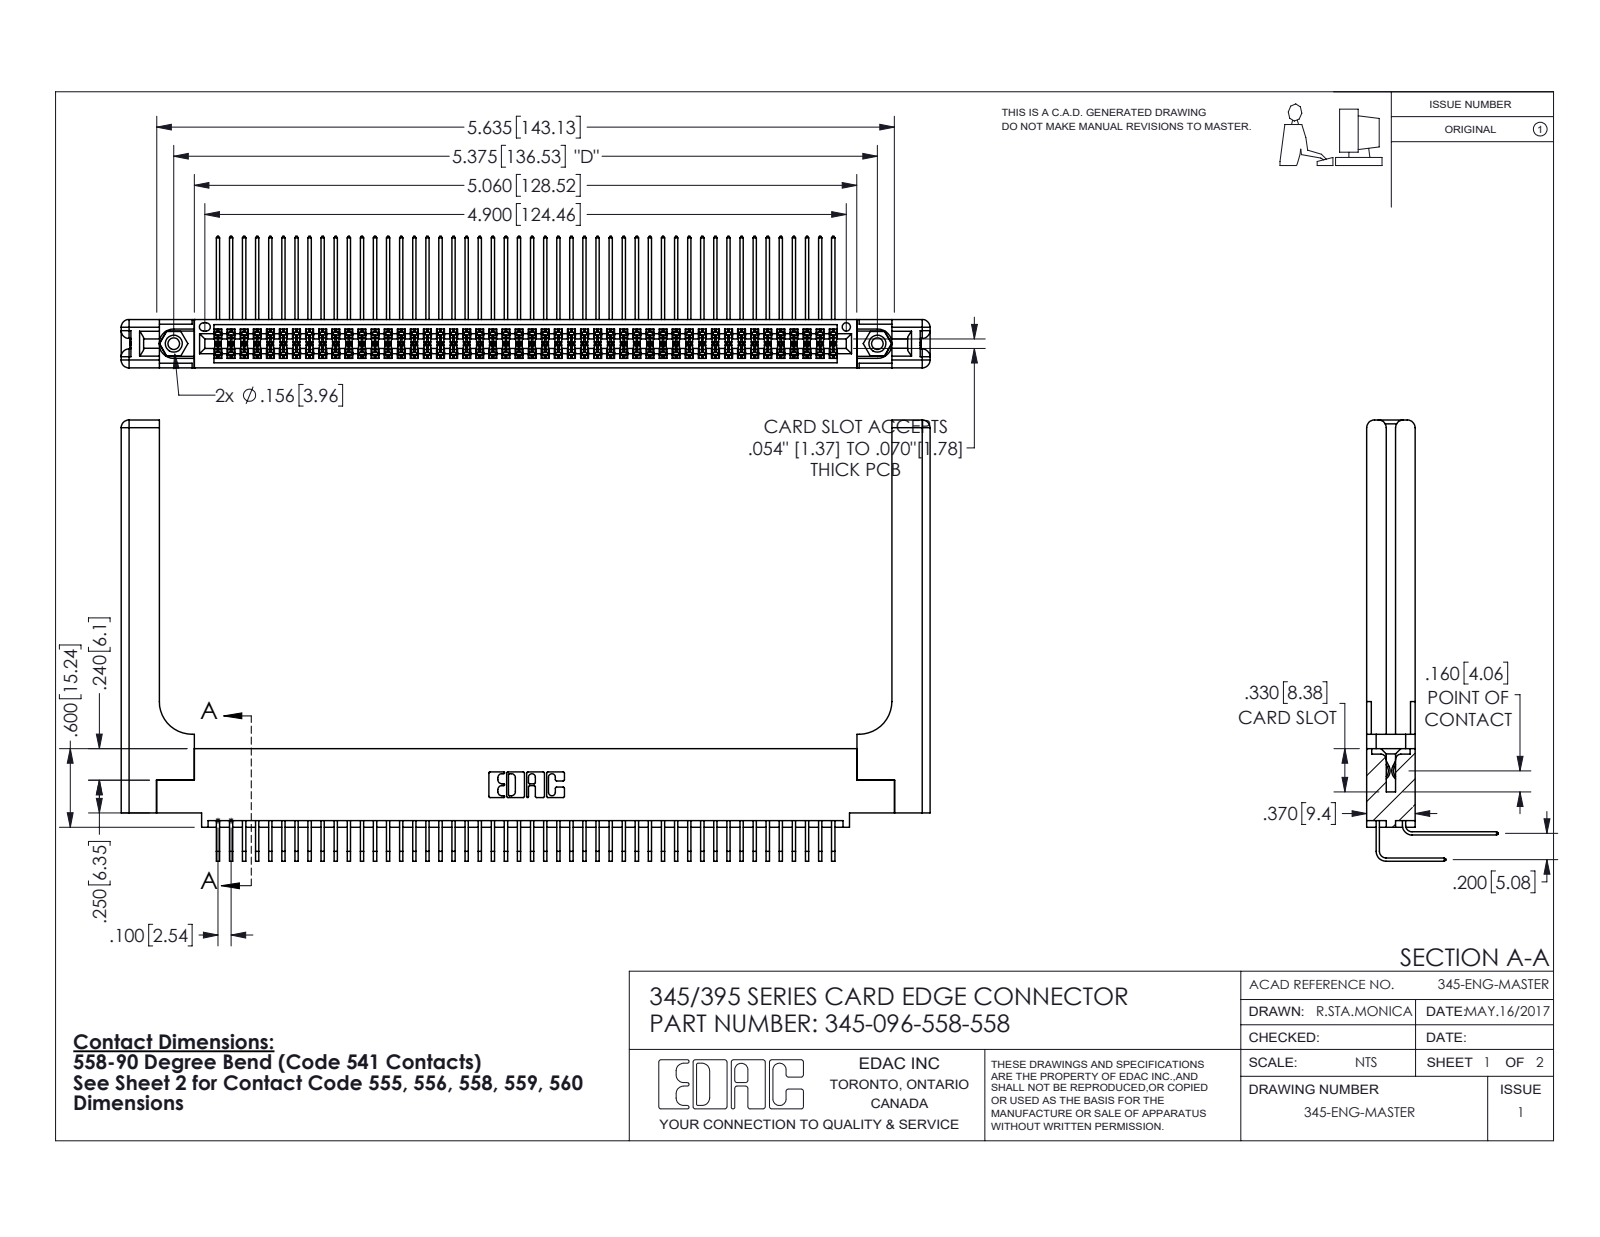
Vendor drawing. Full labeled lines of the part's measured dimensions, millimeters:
Part name (STEP PRODUCT): 345-096-558-558; 345-220-058_345-220-058; 345-250-001_345-250-001-102; 345 Part_0.110 Offset - 0.156 Dia-TH (+2 more)
STEP written by: SolidWorks 2016 (CONFIG_CONTROL_DESIGN)
Units: millimetres
Bodies: 101 solids, 5378 faces (3592 planar, 1726 cylindrical, 60 other)
Overall size (bounding box): 156.9 × 85.6 × 25.5
Volume: 24 250 mm³ · Surface area: 31 200 mm²
Round holes (diameter × count): ⌀2.3 ×2, ⌀3.2 ×2, ⌀4 ×2, ⌀1.6 ×1
Round bosses / shafts (diameter × count): ⌀3.9 ×2
Partial cylindrical surfaces — rounded edges, fillets, slot ends (radius × count): R0.2 ×192, R0.3 ×22, R1.5 ×16, R0.2 ×6, R0.8 ×6, R0.7 ×3, R0.4 ×2, R0.5 ×2
Main face-to-face distances: 1.8, 7.6, 9.4, 5.1, 2.5, 6.9, 0.6, 5.7, 3.8, 3.8
Hole centre spacings: 6.9, 130.5, 136.5
